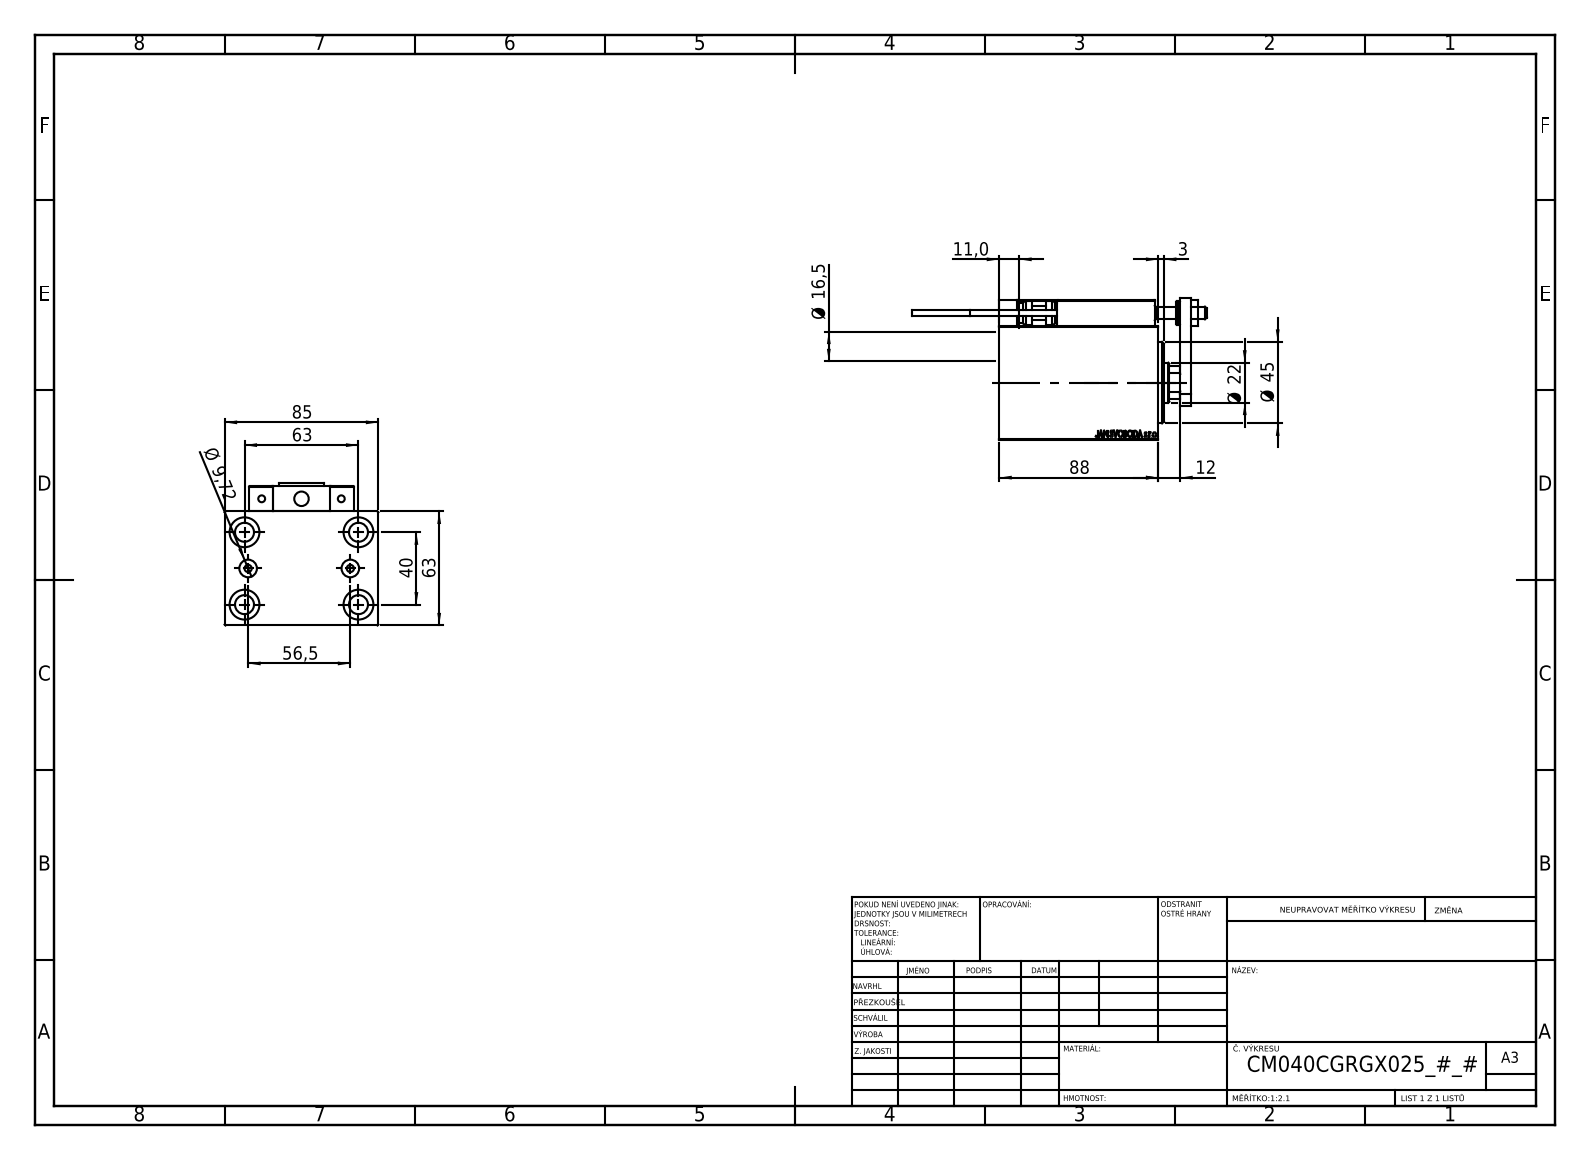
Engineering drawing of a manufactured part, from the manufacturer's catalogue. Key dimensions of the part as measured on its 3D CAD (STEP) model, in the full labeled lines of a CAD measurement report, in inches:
Part name (STEP PRODUCT): ZARAZKA; TYC_L79; ALLEN BOLT D5; MAGNET (+7 more)
STEP written by: SolidWorks 2019 (CONFIG_CONTROL_DESIGN)
Units: inches
Bodies: 23 solids, 1278 faces (560 planar, 184 cylindrical, 534 other)
Overall size (bounding box): 6.406 × 3.346 × 3.091
Volume: 27.94 in³ · Surface area: 159.7 in²
Round holes (diameter × count): ⌀0.157 ×6, ⌀0.315 ×5, ⌀0.65 ×5, ⌀0.126 ×4, ⌀0.413 ×4, ⌀0.197 ×2, ⌀0.383 ×2, ⌀0.276 ×1, ⌀0.492 ×1, ⌀0.866 ×1, ⌀1.004 ×1, ⌀1.575 ×1
Round bosses / shafts (diameter × count): ⌀0.197 ×2, ⌀0.15 ×2, ⌀0.512 ×1, ⌀0.433 ×1
Partial cylindrical surfaces — rounded edges, fillets, slot ends (radius × count): R0.012 ×30, R0.118 ×2, R0.413 ×1
Main face-to-face distances: 2.48, 0.472, 3.346, 2.992, 3.465, 0.551, 3.031, 0.984, 0.591, 0.709
Hole centre spacings: 1.469, 0.448, 0.787, 0.791, 0.807, 1.165, 1.169, 1.42
